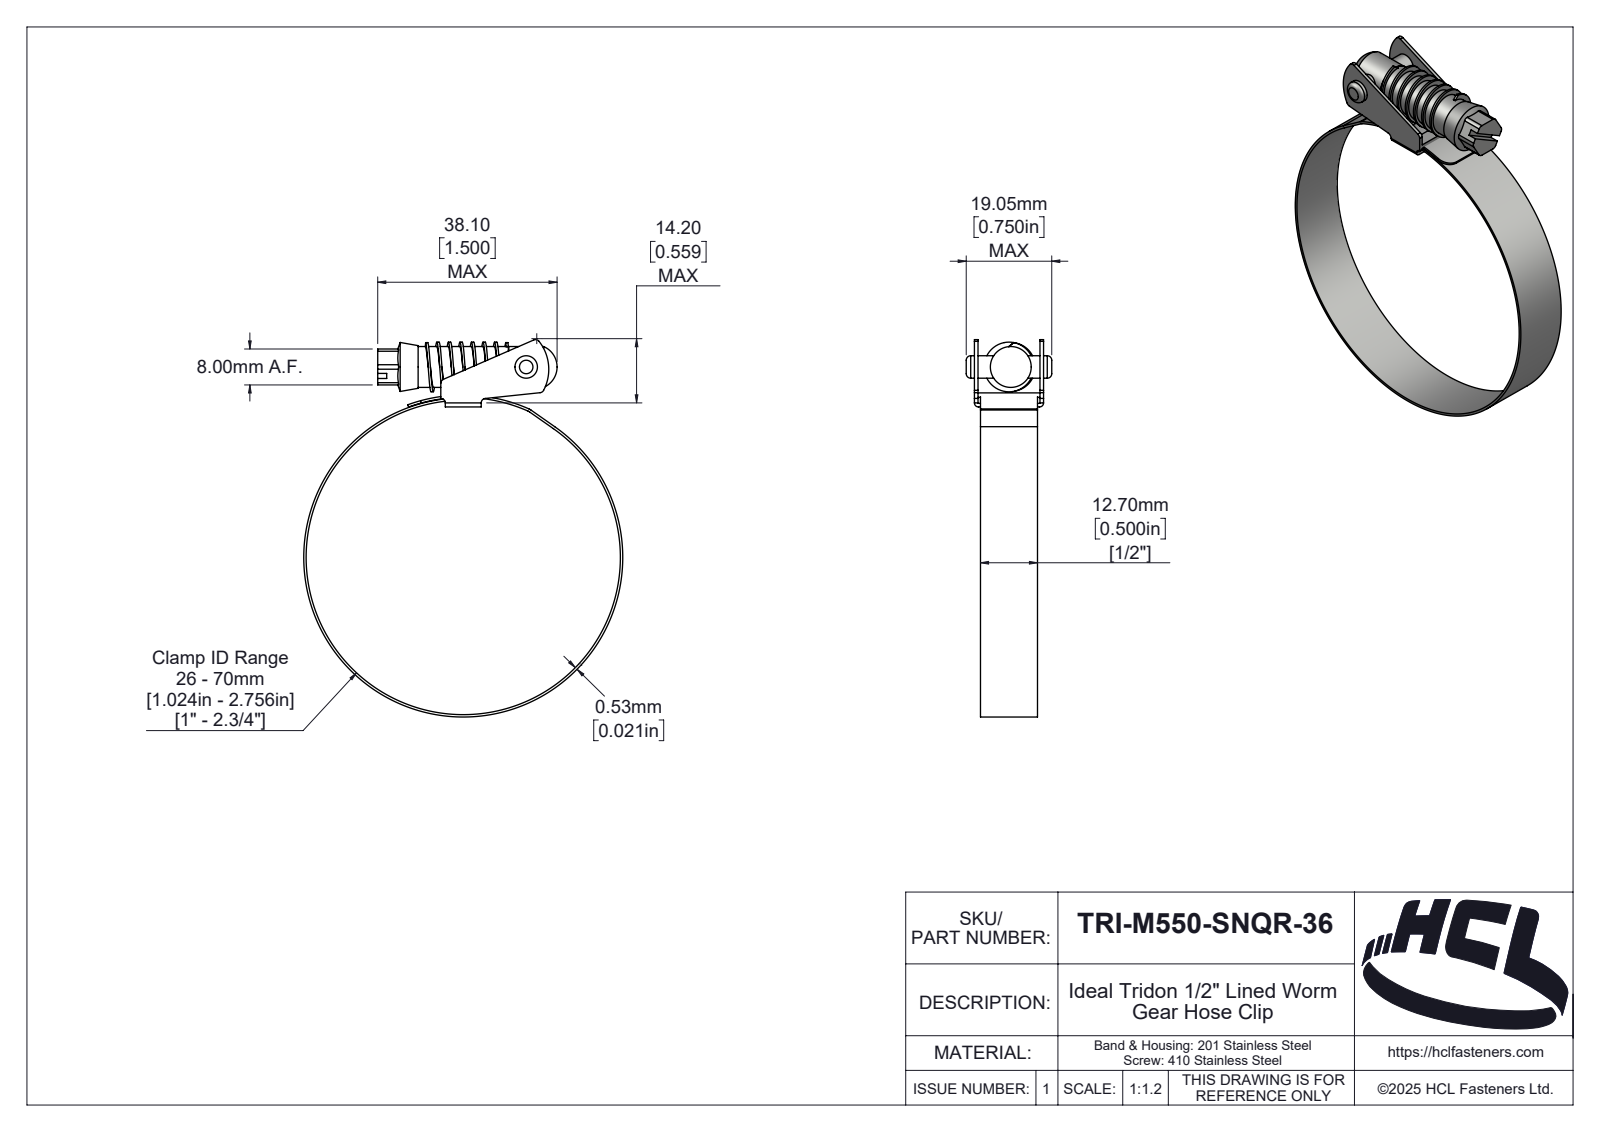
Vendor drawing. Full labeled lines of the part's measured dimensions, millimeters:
Part name (STEP PRODUCT): TRI-M550-SNQR-36
STEP written by: SolidWorks 2025 (AUTOMOTIVE_DESIGN)
Units: millimetres
Bodies: 5 solids, 222 faces (44 planar, 112 cylindrical, 66 other)
Overall size (bounding box): 84.02 × 71.06 × 19.05
Volume: 4 756 mm³ · Surface area: 9 785 mm²
Round holes (diameter × count): ⌀5 ×1, ⌀70 ×1
Round bosses / shafts (diameter × count): ⌀71.06 ×1, ⌀9.1 ×1
Partial cylindrical surfaces — rounded edges, fillets, slot ends (radius × count): R1 ×11, R0.1 ×2, R0.9 ×2, R3 ×2, R0.46 ×1, R1.89 ×1, R2 ×1, R2.35 ×1
Main face-to-face distances: 0.8, 14.6, 1.35, 14.05, 0.55, 13.25, 15.4, 13.8, 12.7, 1
Hole centre spacings: 44.66
